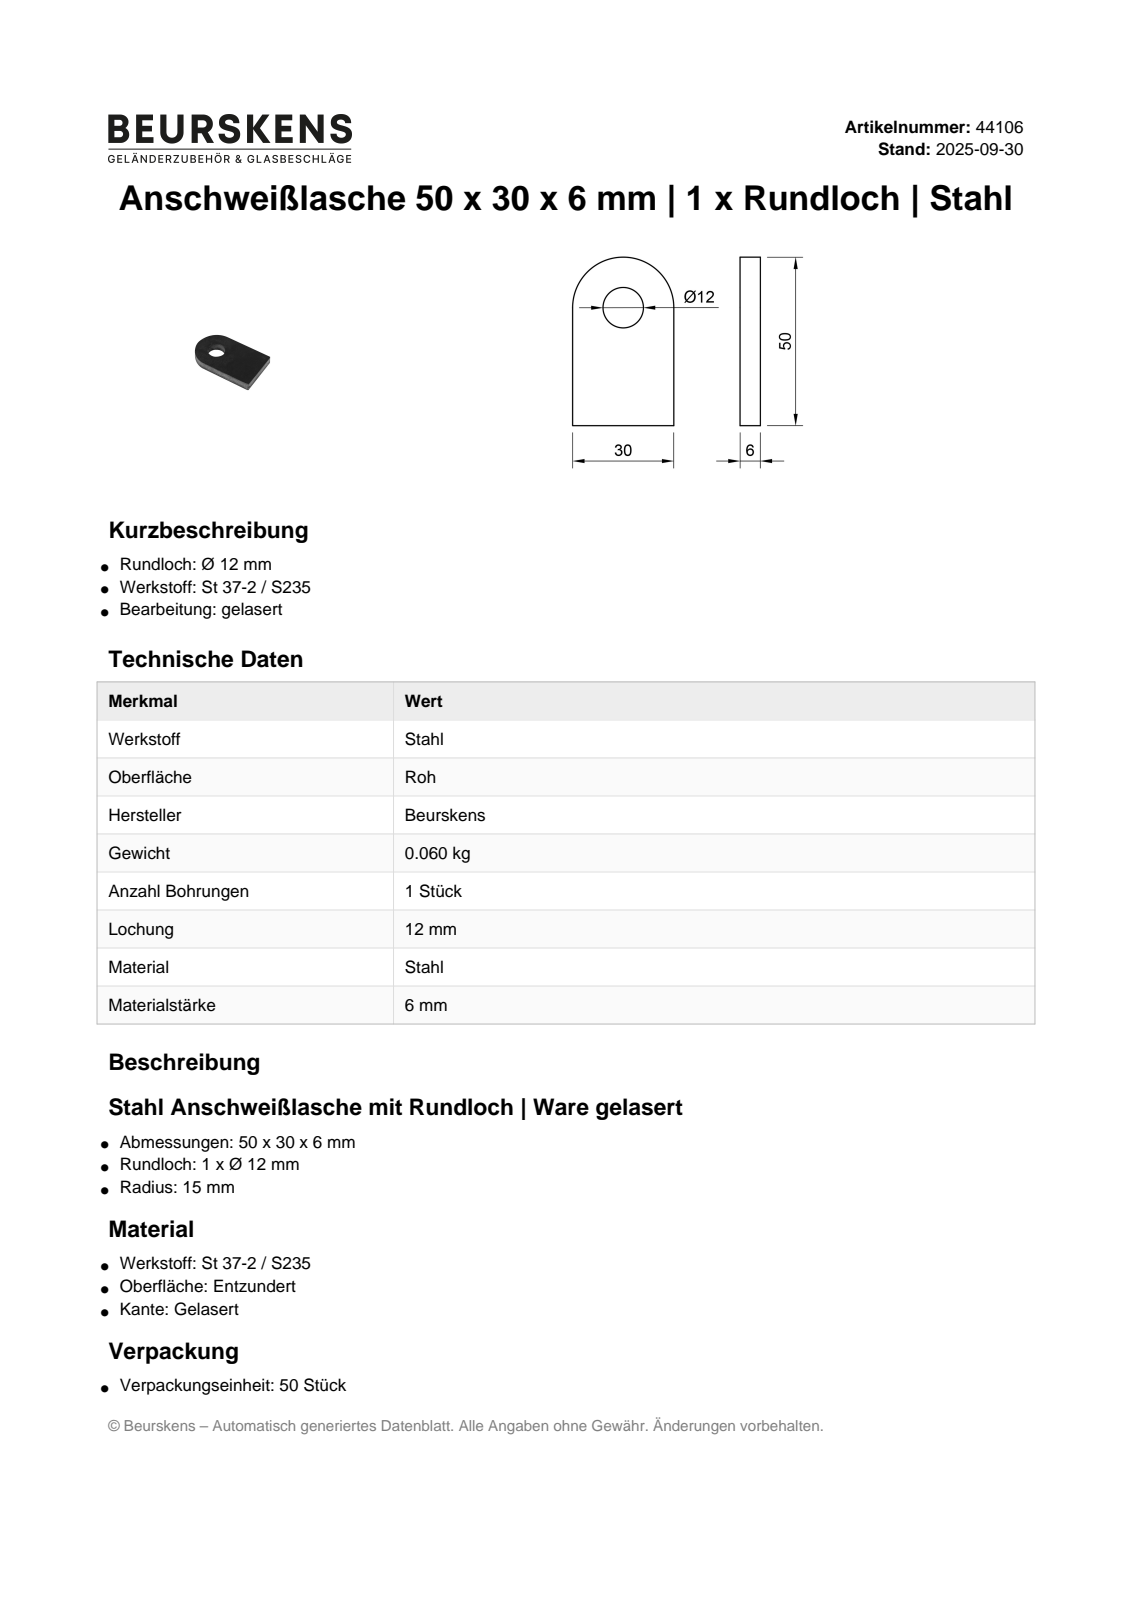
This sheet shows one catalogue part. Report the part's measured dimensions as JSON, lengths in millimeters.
{"part_name": "44106", "step_written_by": "Autodesk Inventor 2023 (AUTOMOTIVE_DESIGN)", "units": "millimeters", "bodies": {"solids": 1, "faces": 7, "planar": 5, "cylindrical": 2, "other": 0}, "overall_size": [50, 30, 6], "volume_mm3": 7742, "surface_area_mm2": 3690, "round_holes": [[12, 1]], "partial_cylinders_radius": [[15, 1]], "face_to_face_distances": [6, 30]}
